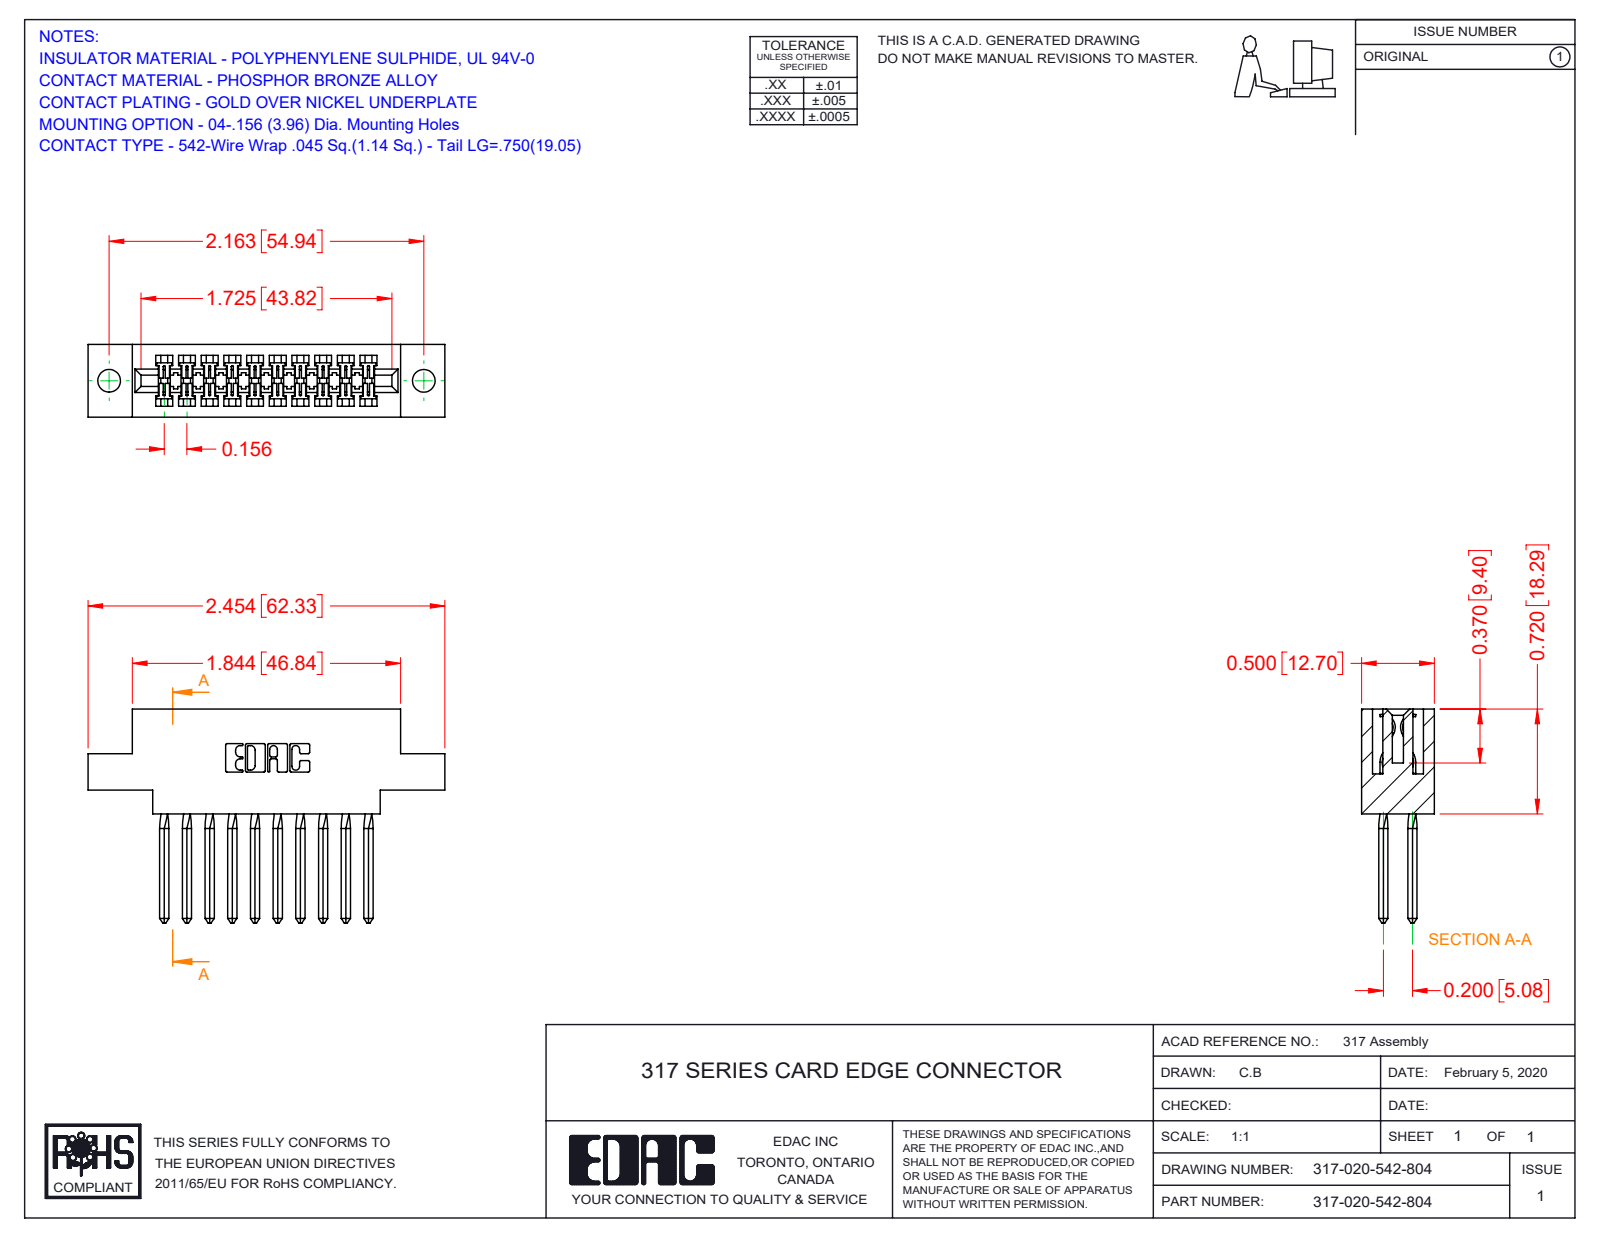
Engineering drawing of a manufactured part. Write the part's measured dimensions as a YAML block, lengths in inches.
part_name: "317-020-542-804; 317-290-003_542; 317 Part_.156 Dia - TH"
step_written_by: "SolidWorks 2016 (CONFIG_CONTROL_DESIGN)"
units: inches
bodies: {solids: 21, faces: 1242, planar: 978, cylindrical: 184, other: 80}
overall_size: [2.454, 1.47, 0.5]
volume: 0.556
surface_area: 17.76
round_holes:
  - {diameter: 0.156, count: 2}
partial_cylinders:
  - {radius: 0.006, count: 40}
  - {radius: 0.01, count: 22}
  - {radius: 0.007, count: 6}
  - {radius: 0.031, count: 6}
  - {radius: 0.026, count: 3}
  - {radius: 0.074, count: 2}
  - {radius: 0.089, count: 2}
  - {radius: 0.1, count: 2}
face_to_face_distances: [0.5, 0.075, 0.425, 0.11, 0.22, 0.116, 0.35, 0.156, 0.2, 0.331]
hole_center_spacings: [2.163]
